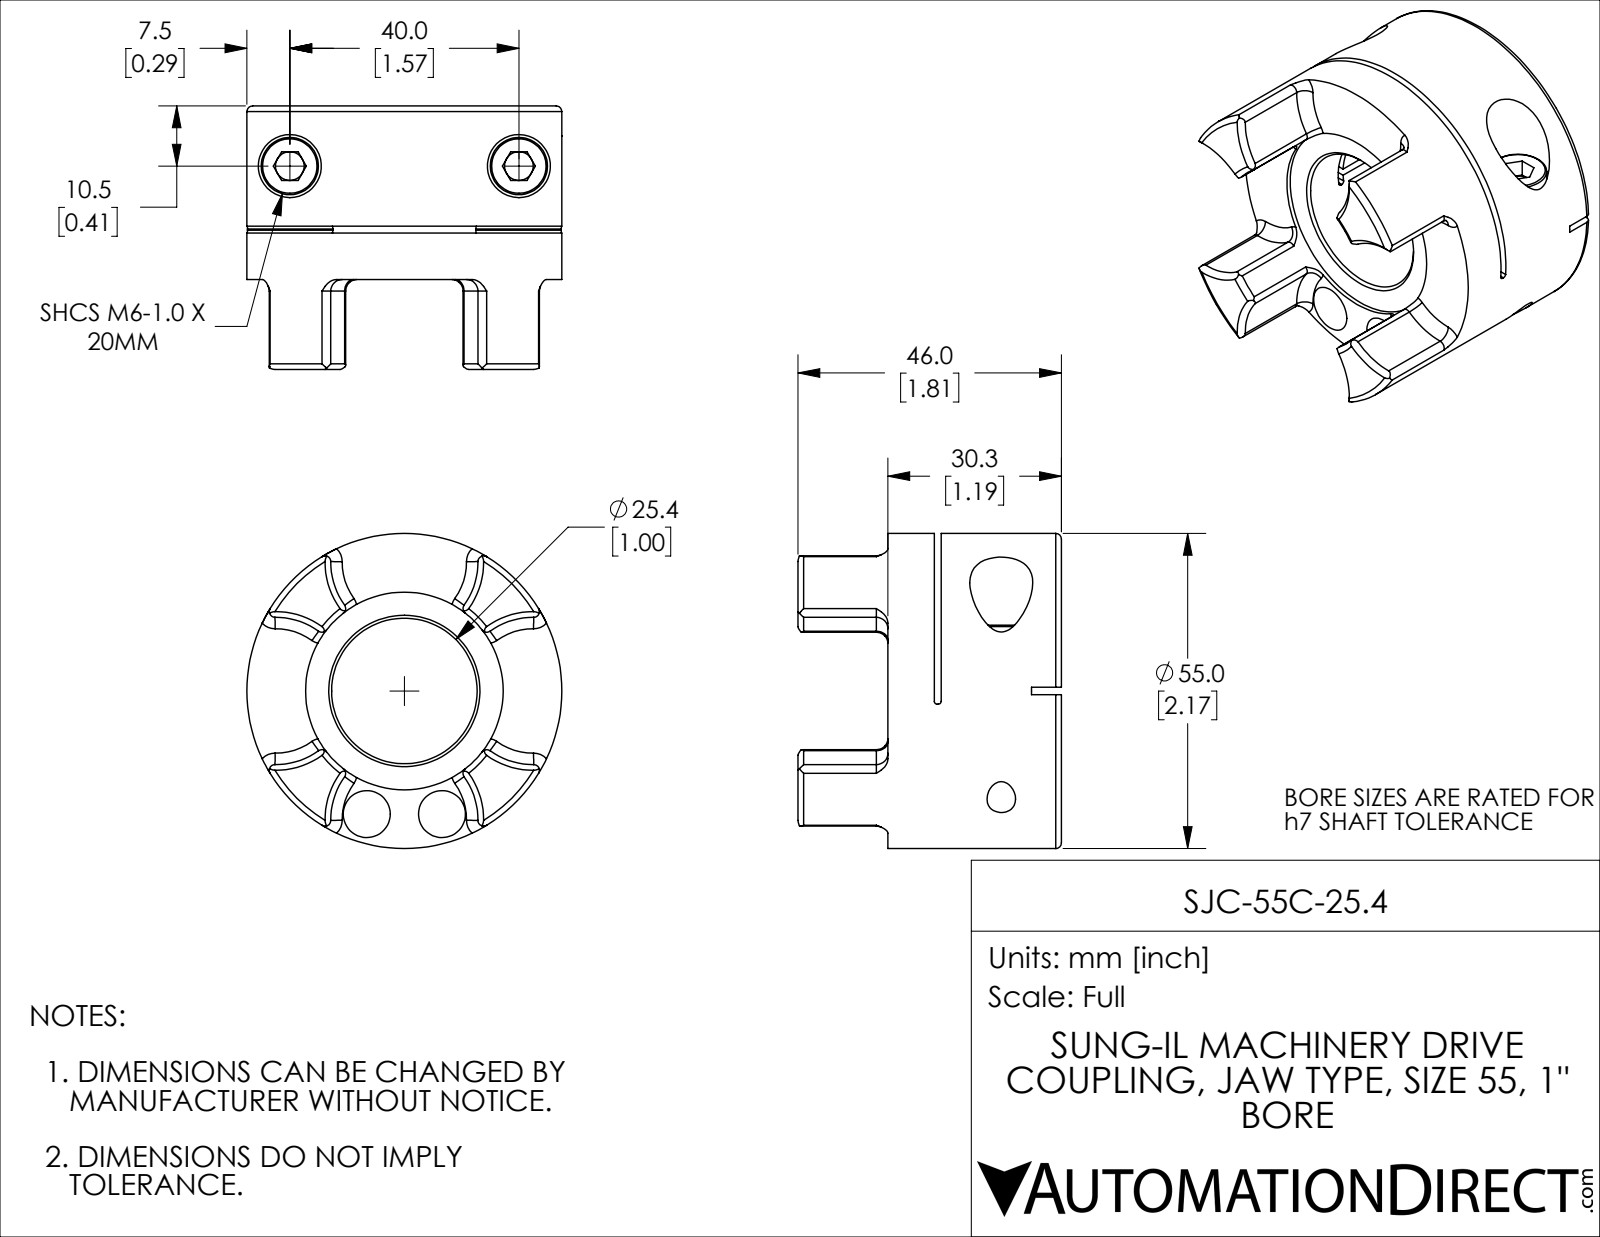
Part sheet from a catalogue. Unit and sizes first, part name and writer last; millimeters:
Units: millimetres
Overall size (bounding box): 55 × 55 × 46
Round holes (diameter × count): ⌀5 ×2, ⌀6.4 ×2, ⌀8.2 ×2, ⌀11 ×2, ⌀25 ×1, ⌀34.5 ×1
Round bosses / shafts (diameter × count): ⌀10 ×2, ⌀6 ×2, ⌀55 ×1
Partial cylindrical surfaces — rounded edges, fillets, slot ends (radius × count): R1 ×16, R12.85 ×4, R0.5 ×2, R50 ×1
Main face-to-face distances: 22.2, 1.2, 21, 8.1, 9.3, 30.3, 1.3, 0.8, 7.3, 8.5
Hole centre spacings: 22.47, 13.14, 40
Volume: 58 276 mm³ · Surface area: 19 900 mm²
Bodies: 3 solids, 206 faces (52 planar, 72 cylindrical, 82 other)
Part name (STEP PRODUCT): SJC-55C-25
STEP written by: SolidWorks 2021 (CONFIG_CONTROL_DESIGN)
